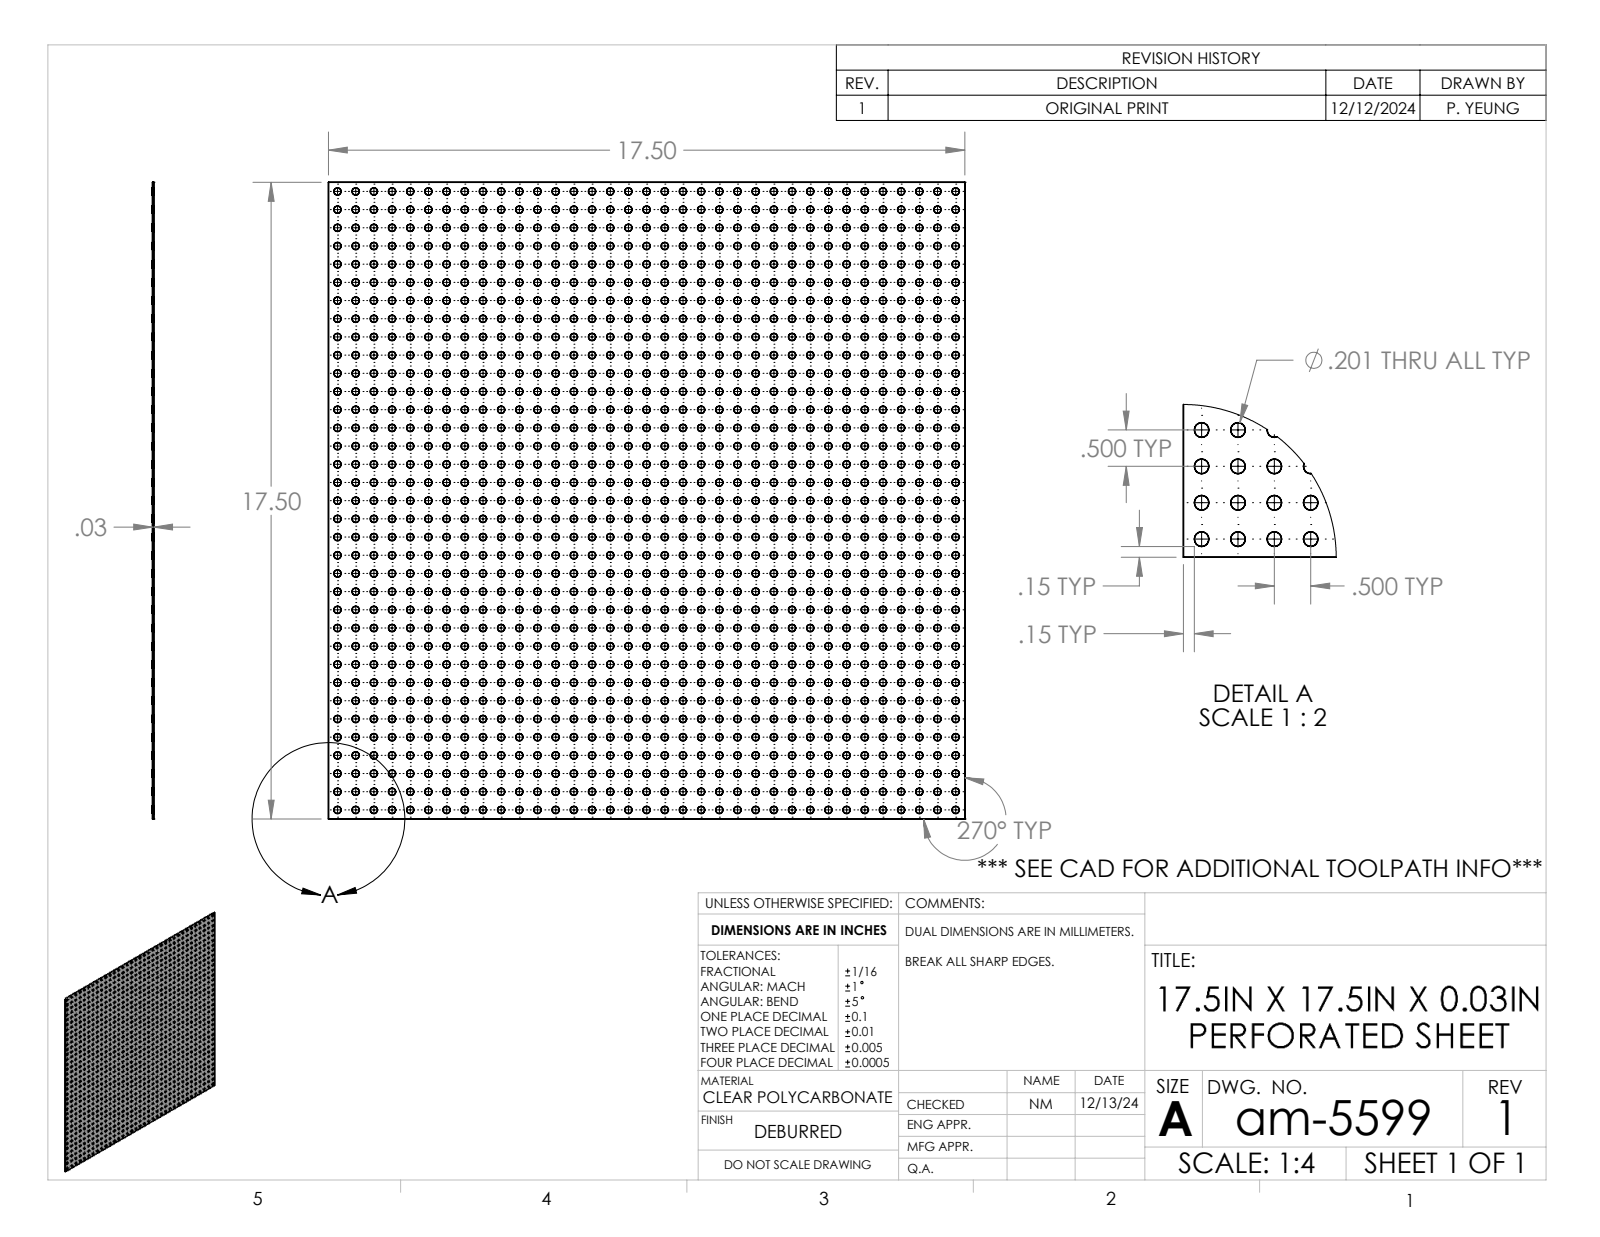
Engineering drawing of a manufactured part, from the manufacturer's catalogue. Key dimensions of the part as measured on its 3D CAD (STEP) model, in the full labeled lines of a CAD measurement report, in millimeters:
Part name (STEP PRODUCT): am-5599 17.5IN x 17.5IN x 0.03IN Perforated Sheet
STEP written by: SolidWorks 2024 (AUTOMOTIVE_DESIGN)
Units: millimetres
Bodies: 1 solid, 2456 faces (6 planar, 2450 cylindrical, 0 other)
Overall size (bounding box): 444.5 × 444.5 × 0.8
Volume: 136 900 mm³ · Surface area: 362 000 mm²
Round holes (diameter × count): ⌀5.1 ×1225
Main face-to-face distances: 0.8, 444.5
Hole centre spacings: 12.7, 25.4, 38.1, 50.8, 63.5, 76.2, 88.9, 101.6
